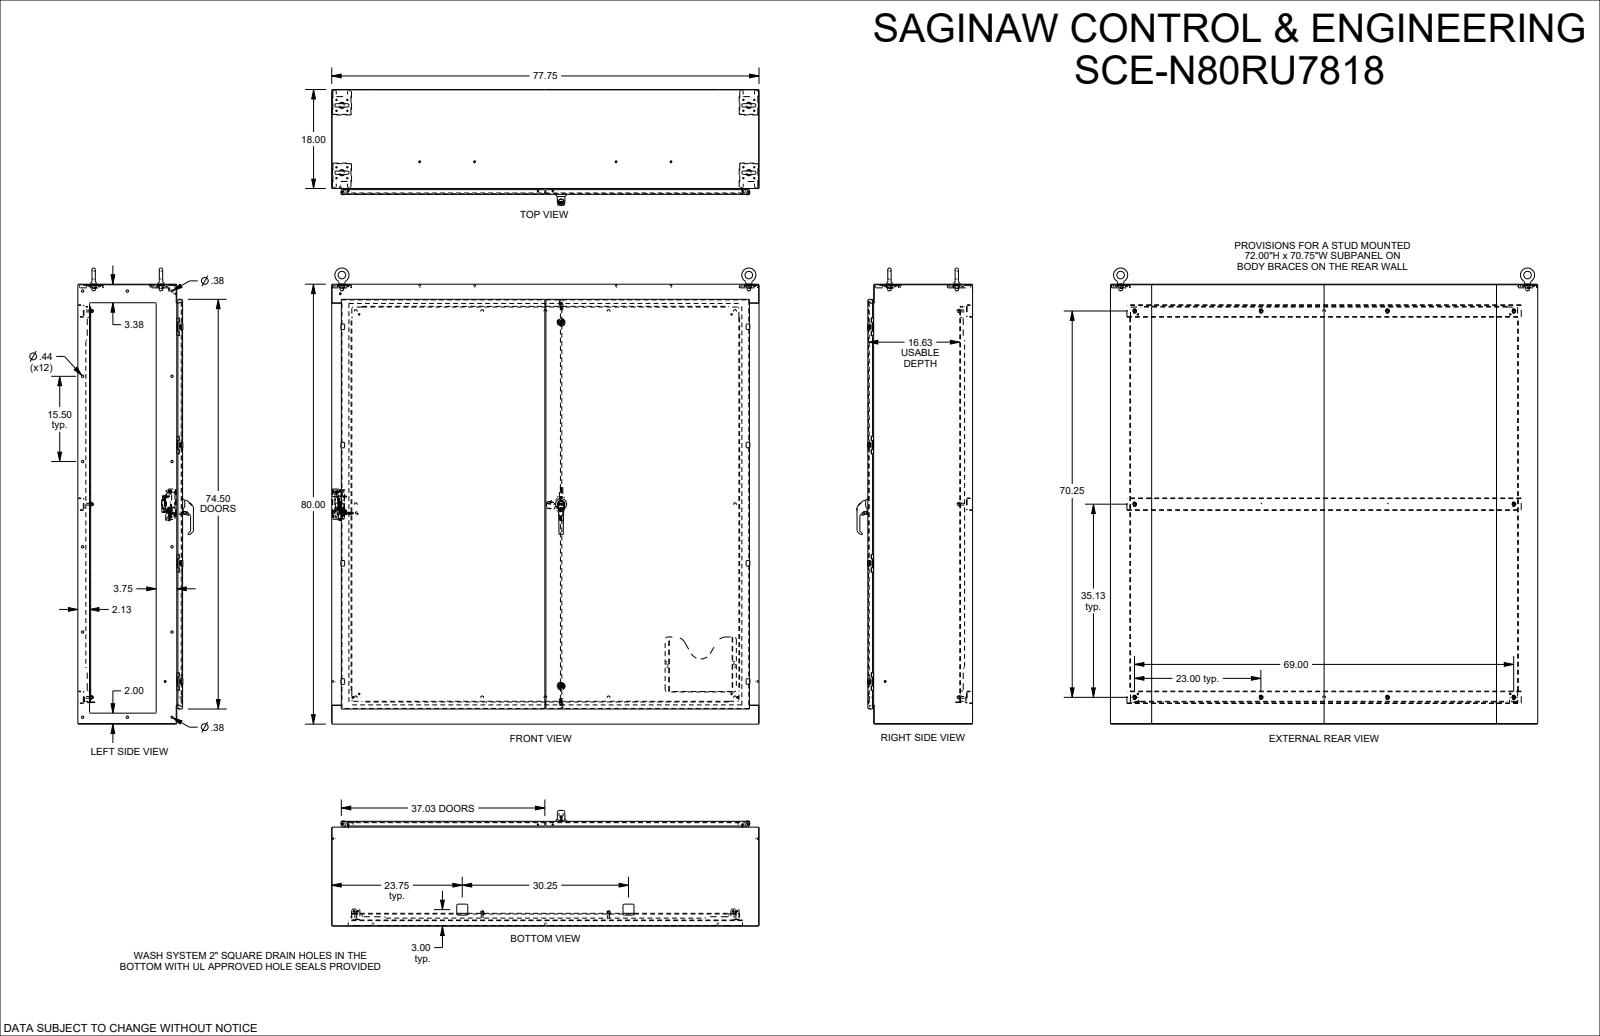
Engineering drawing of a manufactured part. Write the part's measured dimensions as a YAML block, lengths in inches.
part_name: "SCE-N80RU7818"
step_written_by: "SolidWorks 2023 (AUTOMOTIVE_DESIGN)"
units: inches
bodies: {solids: 35, faces: 5049, planar: 2384, cylindrical: 1657, other: 1008}
overall_size: [82.945, 77.75, 21.046]
volume: 2042
surface_area: 39168
round_holes:
  - {diameter: 0.25, count: 19}
  - {diameter: 0.375, count: 18}
  - {diameter: 0.205, count: 16}
  - {diameter: 0.244, count: 16}
  - {diameter: 0.437, count: 12}
  - {diameter: 0.04, count: 8}
  - {diameter: 0.218, count: 8}
  - {diameter: 0.17, count: 4}
  - {diameter: 0.256, count: 4}
  - {diameter: 0.875, count: 4}
  - {diameter: 0.206, count: 2}
  - {diameter: 0.343, count: 2}
round_bosses_or_shafts:
  - {diameter: 0.17, count: 24}
  - {diameter: 0.25, count: 16}
  - {diameter: 0.24, count: 16}
  - {diameter: 0.196, count: 10}
  - {diameter: 1.173, count: 4}
  - {diameter: 0.6, count: 4}
  - {diameter: 1.4, count: 2}
  - {diameter: 0.406, count: 2}
partial_cylinders:
  - {radius: 0.03, count: 102}
  - {radius: 0.015, count: 88}
  - {radius: 0.125, count: 67}
  - {radius: 0.04, count: 41}
  - {radius: 0.167, count: 38}
  - {radius: 0.062, count: 34}
  - {radius: 0.063, count: 32}
  - {radius: 0.229, count: 32}
face_to_face_distances: [0.104, 18.954, 18.85, 19.058, 79.896, 17.896, 1.058, 80, 79.792, 77.646]
hole_center_spacings: [21.5, 1.979, 43, 72.868, 1.4, 15.5, 22.457, 75.934]
